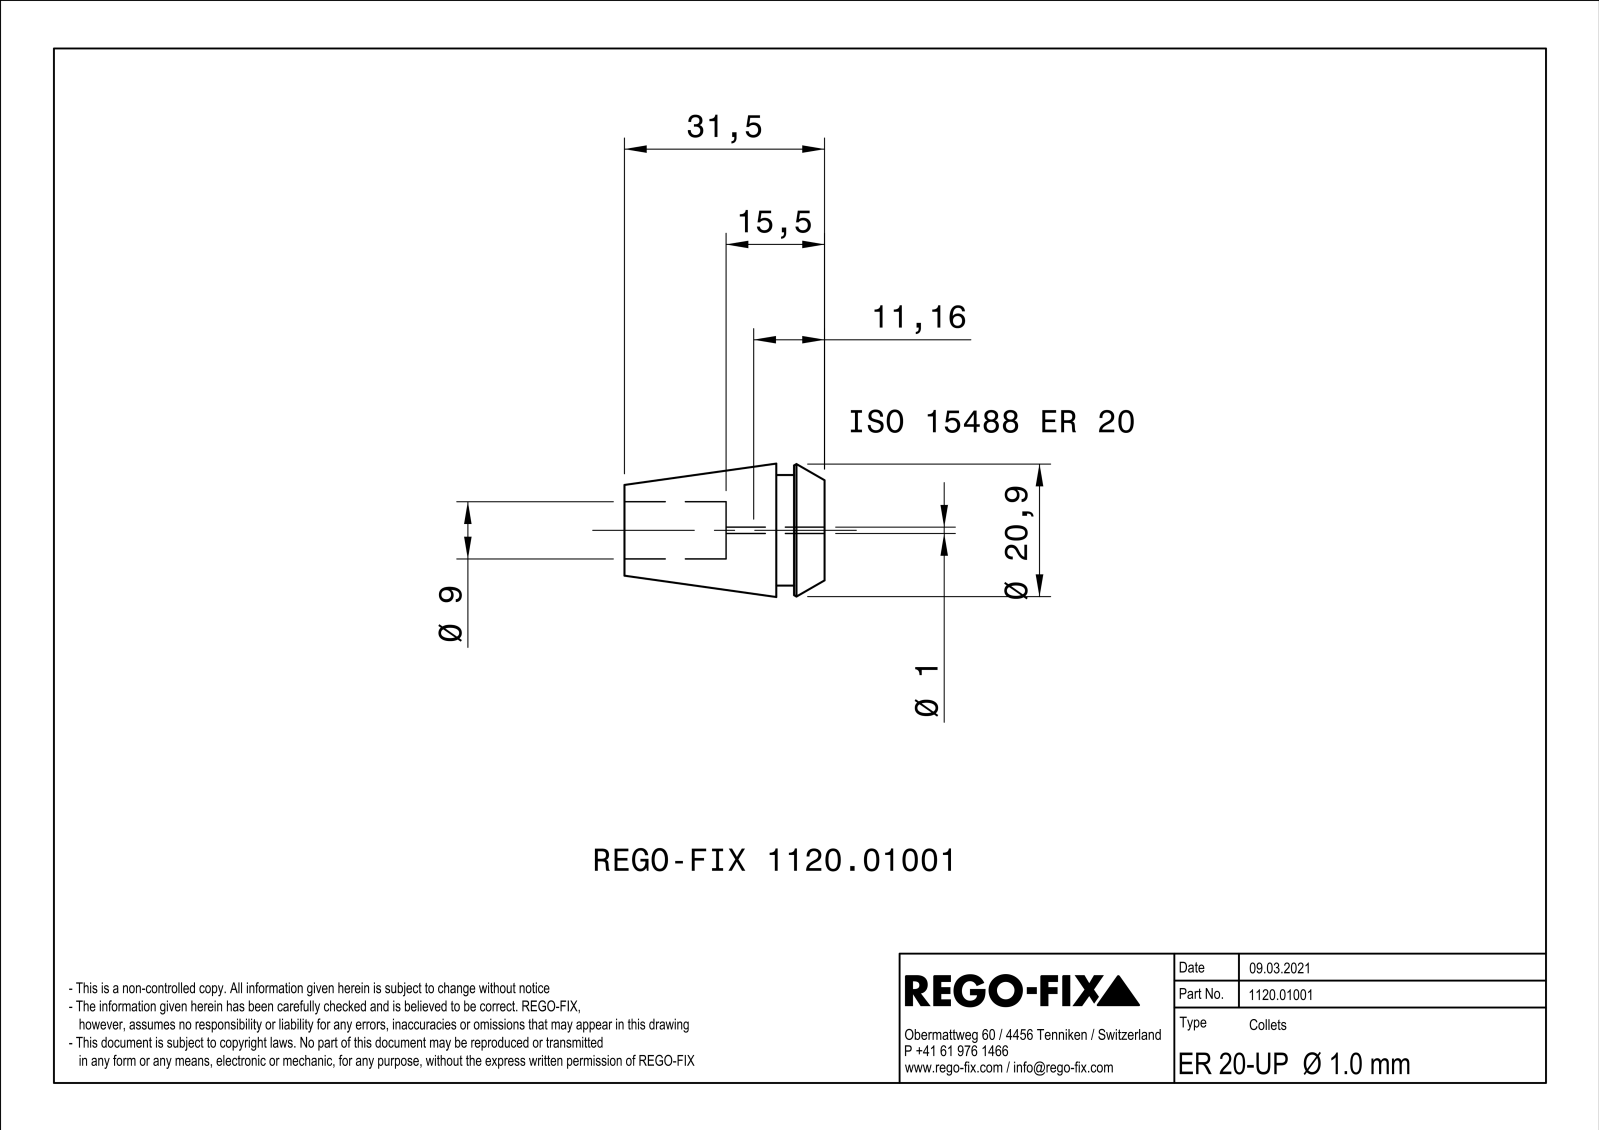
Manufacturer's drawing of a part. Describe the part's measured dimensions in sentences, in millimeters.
The part is named "NOCUT". Its 3-D file was written by "SIEMENS PLM Software Solid Edge ST10 (AUTOMOTIVE_DESIGN)". It is 1 solid with 245 faces: 100 planar, 41 cylindrical and 104 other. Overall it measures 31.5 by 21 by 21 millimeters. Its volume is 5 886 cubic millimeters and its surface area 6 780 square millimeters. Round holes: 1 of diameter 9. Round bosses or shafts: 1 of diameter 17.4. Partial cylindrical surfaces (rounded edges, fillets, slot ends): 8 of radius 35, 1 of radius 0.5. The main face-to-face distances are 0.45, 0.44, 0.46, 7.6, 4.8, 2.8, 31.5, 26.7, 23.9, 15.5.
